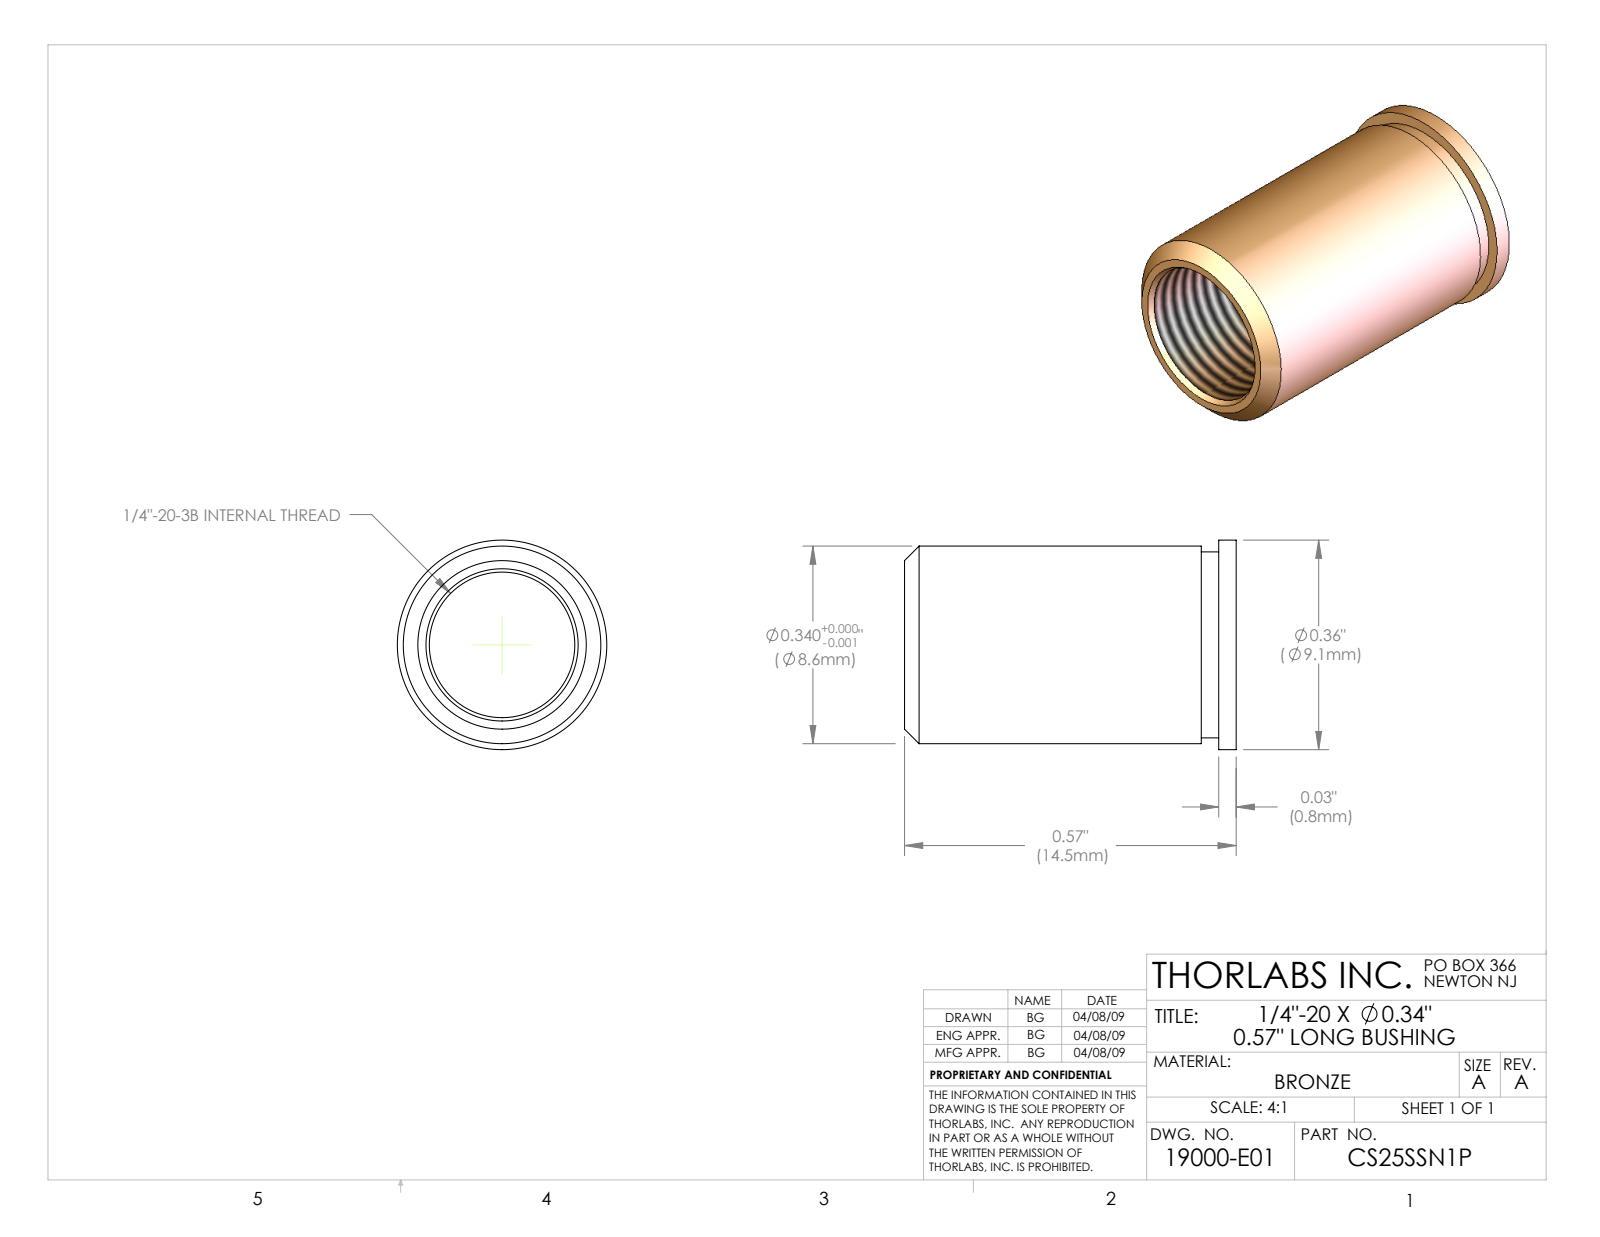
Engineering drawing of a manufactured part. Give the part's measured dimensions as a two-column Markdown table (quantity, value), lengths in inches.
| quantity | value |
| --- | --- |
| part name | 19000-E0W |
| STEP written by | SolidWorks 2007 (AUTOMOTIVE_DESIGN) |
| units | inches |
| bodies | 1 solid, 18 faces (4 planar, 8 cylindrical, 6 other) |
| overall size | 0.57 × 0.36 × 0.36 |
| volume | 0.023 in³ |
| surface area | 1.16 in² |
| round holes (diameter × count) | 0.25 × 1 |
| round bosses / shafts (diameter × count) | 0.36 × 1, 0.339 × 1, 0.32 × 1 |
| main face-to-face distances | 0.03, 0.57, 0.54, 0.06, 0.03, 0.51 |
